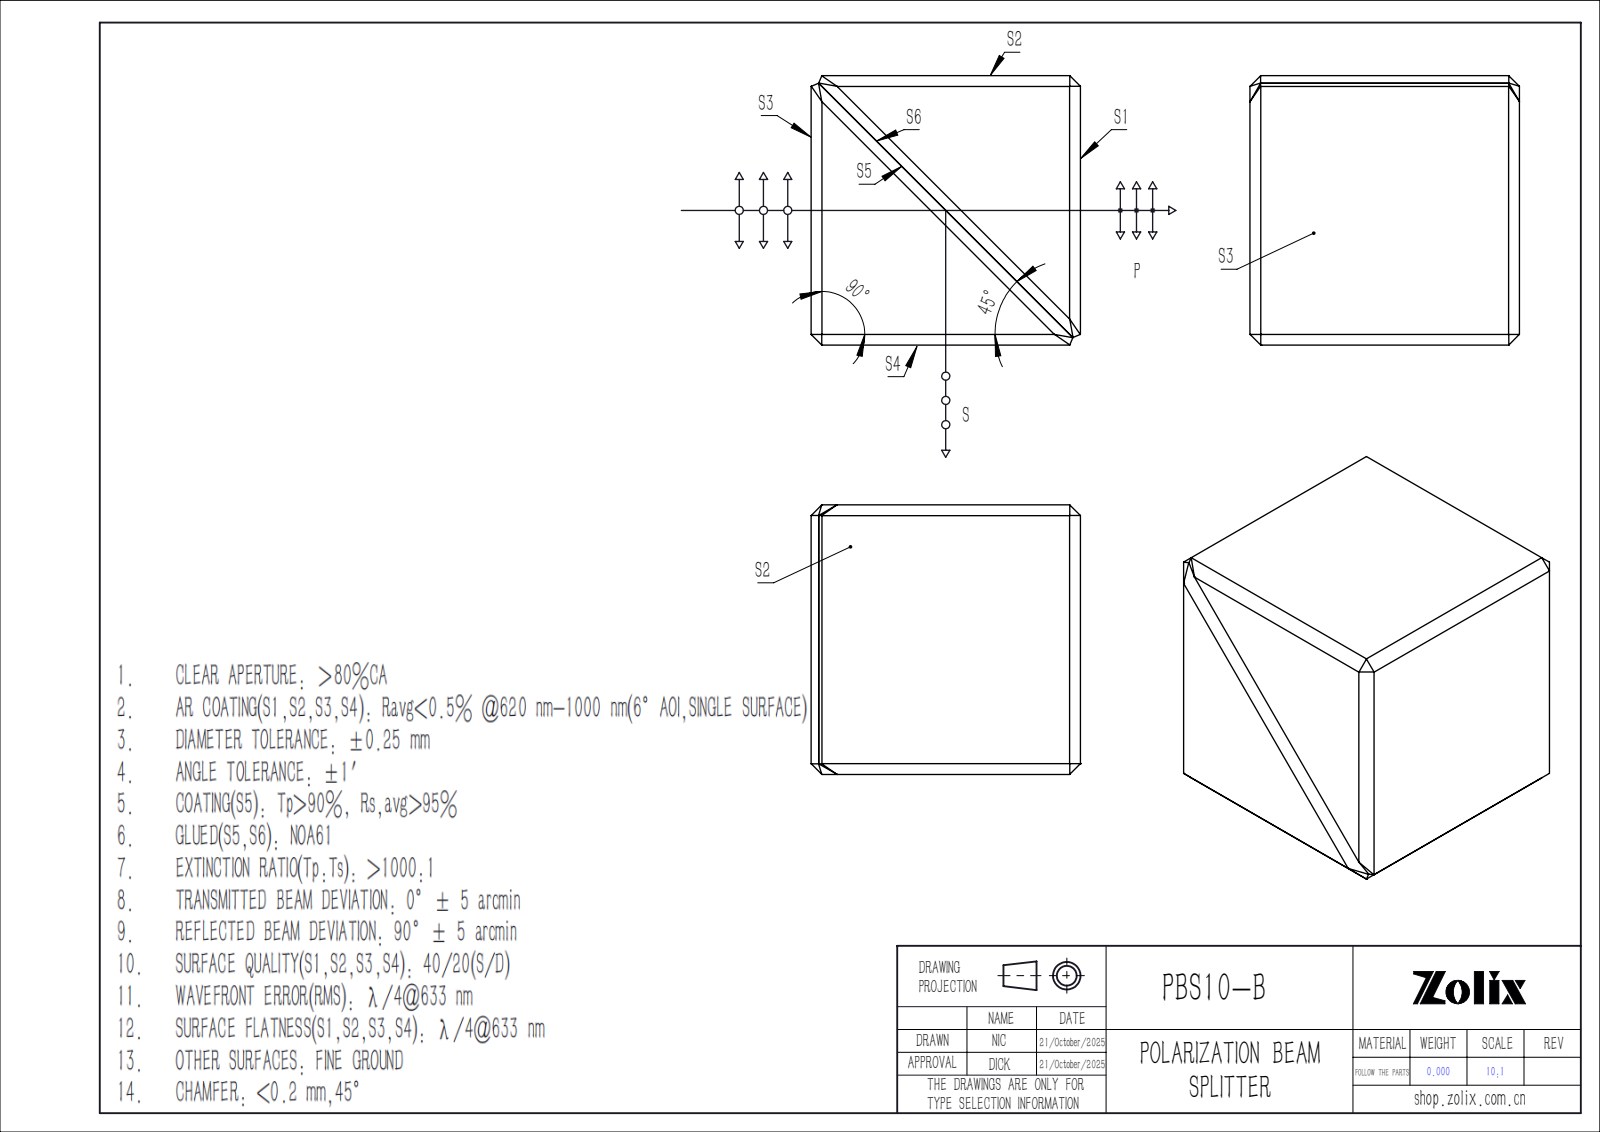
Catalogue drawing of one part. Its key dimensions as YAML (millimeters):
part_name: "PBS612-1-2; PBS612-1-1; PBS612"
step_written_by: "SolidWorks 2022 (CONFIG_CONTROL_DESIGN)"
units: millimeters
bodies: {solids: 2, faces: 43, planar: 41, cylindrical: 2, other: 0}
overall_size: [10, 10, 10]
volume: 996
surface_area: 854
round_holes:
  - {diameter: 0.2, count: 1}
face_to_face_distances: [10, 13.86, 6.79, 12.7, 6.93, 6.92, 13.85, 14.7, 16.85, 14.69]
